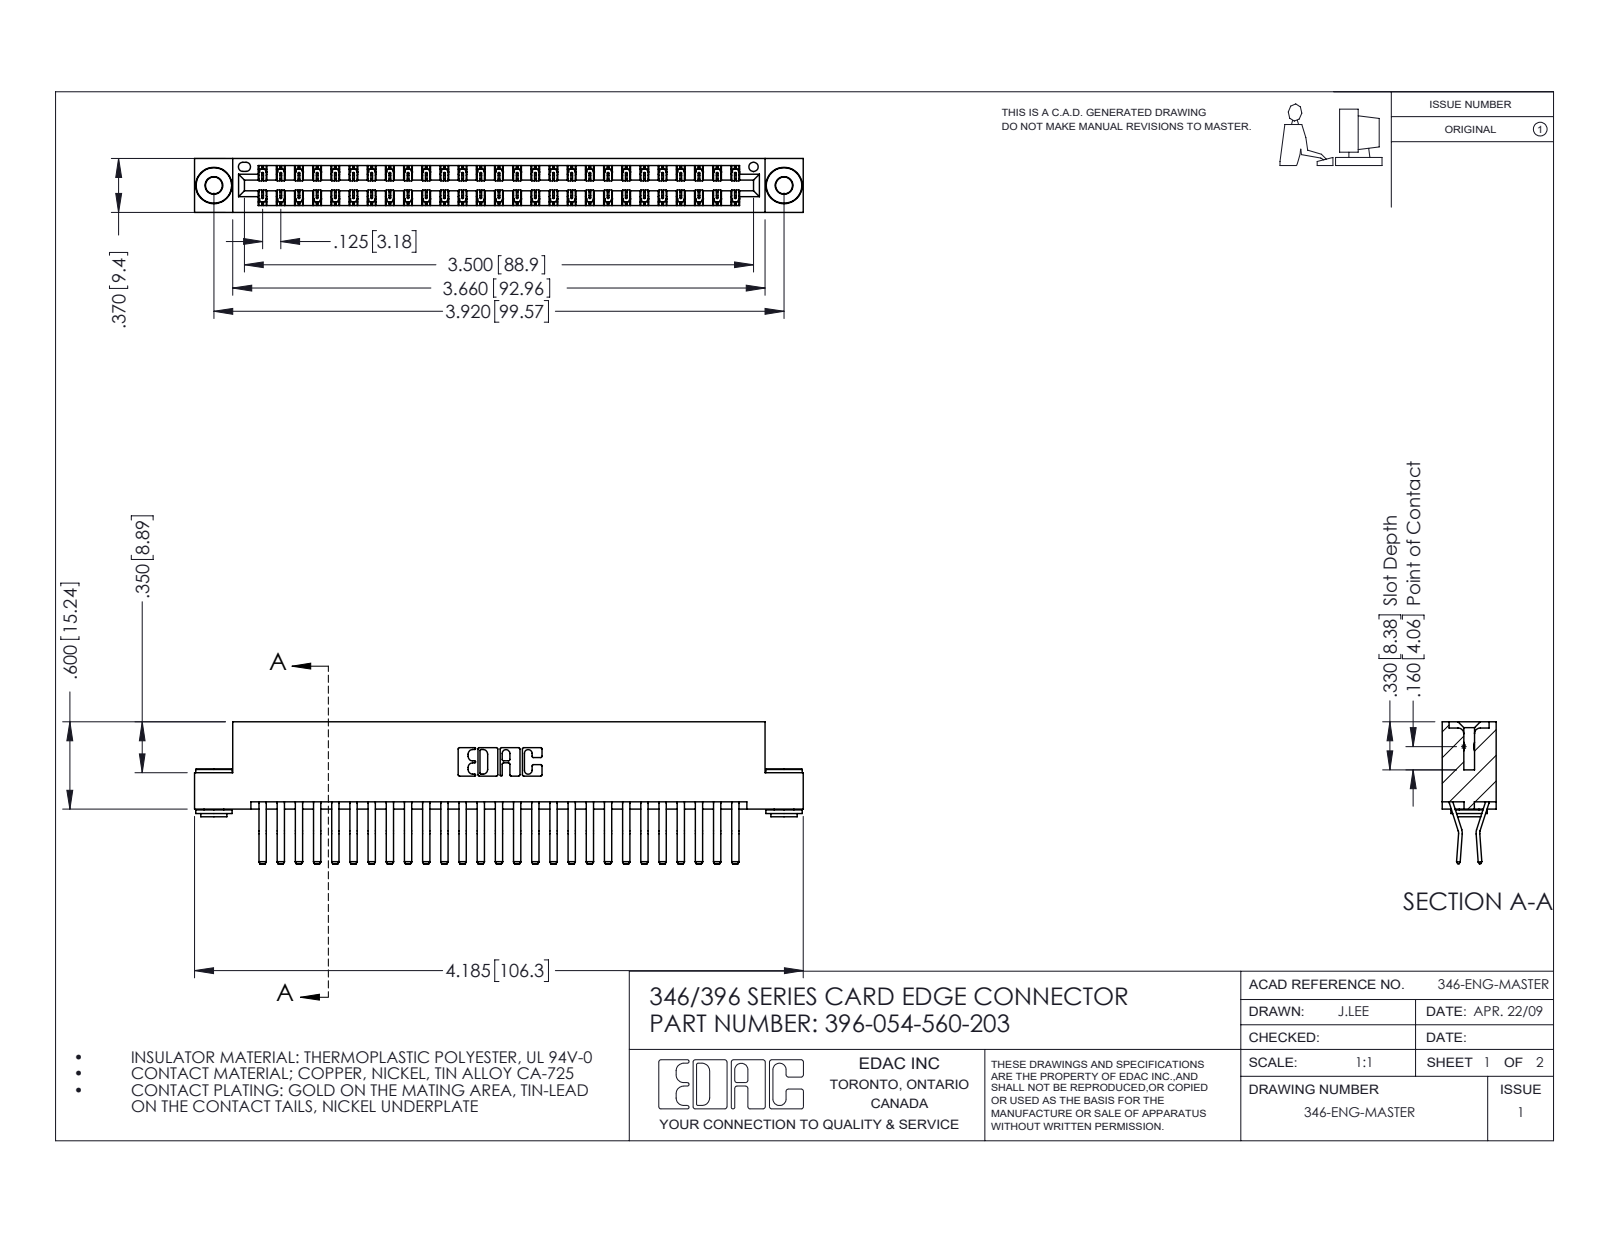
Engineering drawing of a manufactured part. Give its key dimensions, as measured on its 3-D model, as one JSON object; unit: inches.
{"part_name": "345-250-002_345-250-002-102; 346 Part_Flush Mounting Lugs - 0.156 Dia-TH; 345-292-001_560 Tail; 396-054-560-203", "step_written_by": "SolidWorks 2016 (CONFIG_CONTROL_DESIGN)", "units": "inches", "bodies": {"solids": 57, "faces": 3076, "planar": 1976, "cylindrical": 1092, "other": 8}, "overall_size": [4.185, 0.975, 0.37], "volume_in3": 0.648, "surface_area_in2": 24.06, "round_holes": [[0.116, 2], [0.156, 2], [0.064, 1]], "round_bosses_or_shafts": [[0.25, 2], [0.18, 2], [0.136, 2]], "partial_cylinders_radius": [[0.006, 81], [0.01, 22], [0.007, 6], [0.031, 6], [0.026, 3], [0.01, 2], [0.014, 2], [0.022, 2]], "face_to_face_distances": [0.048, 0.322, 0.25, 0.37, 0.025, 0.072, 0.298, 0.275, 0.148, 0.222], "hole_center_spacings": [0.246, 3.712, 3.92]}
